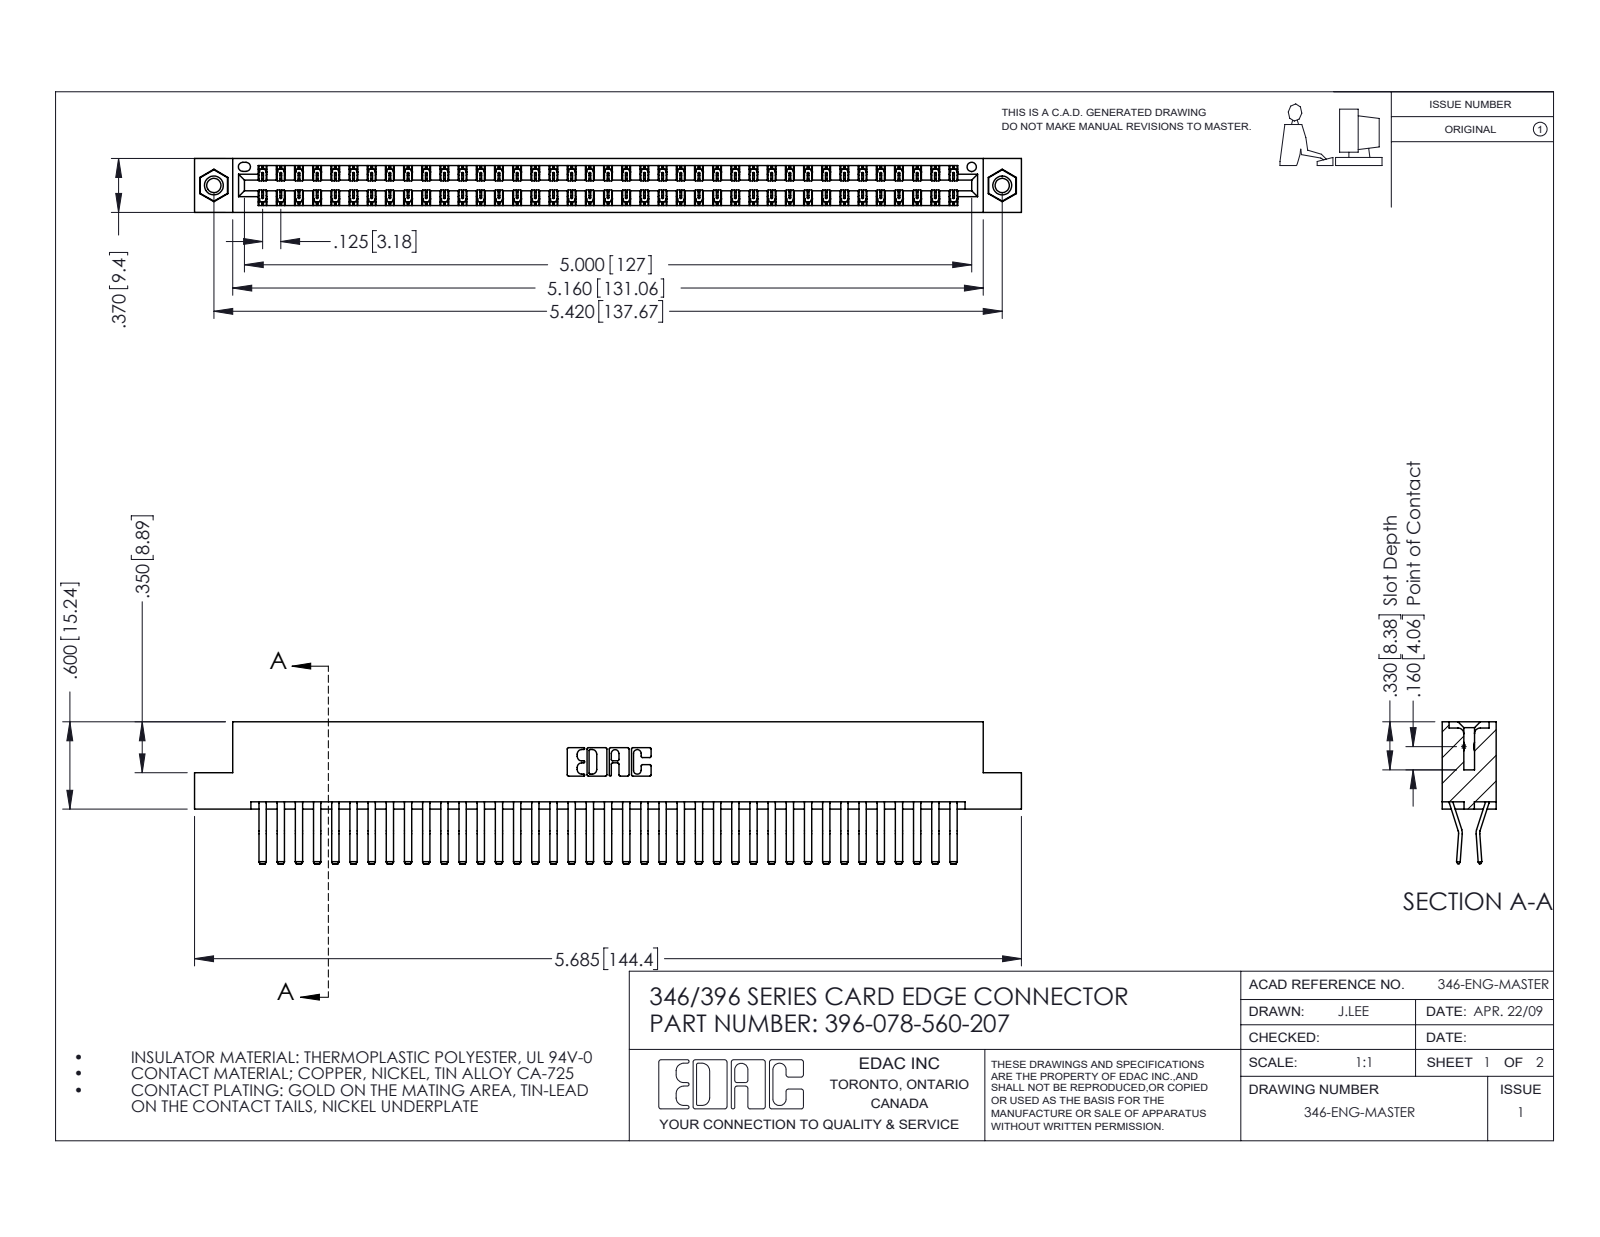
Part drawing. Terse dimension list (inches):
name: 396-078-560-207; 345-250-001_345-250-005-103; 345-292-001_560 Tail; 346 Part_Flush Mounting Lugs - 0.156 Dia-TI
written by: SolidWorks 2016 (CONFIG_CONTROL_DESIGN)
unit: in
bodies: 81 solids, 4394 faces (2838 planar, 1540 cylindrical, 16 other)
size: 5.685 × 0.975 × 0.37
volume: 0.888 in³; area: 33.1 in²
holes: 2× ⌀0.098, 2× ⌀0.125, 2× ⌀0.156, 1× ⌀0.064
bosses: 2× ⌀0.155
rounds: 117× R0.006, 22× R0.01, 6× R0.007, 6× R0.031, 3× R0.026, 2× R0.01, 2× R0.014, 2× R0.022
face distances: 0.048, 0.322, 0.37, 0.025, 0.25, 0.072, 0.298, 0.275, 0.148, 0.222
hole spacings: 0.246, 5.211, 5.42
